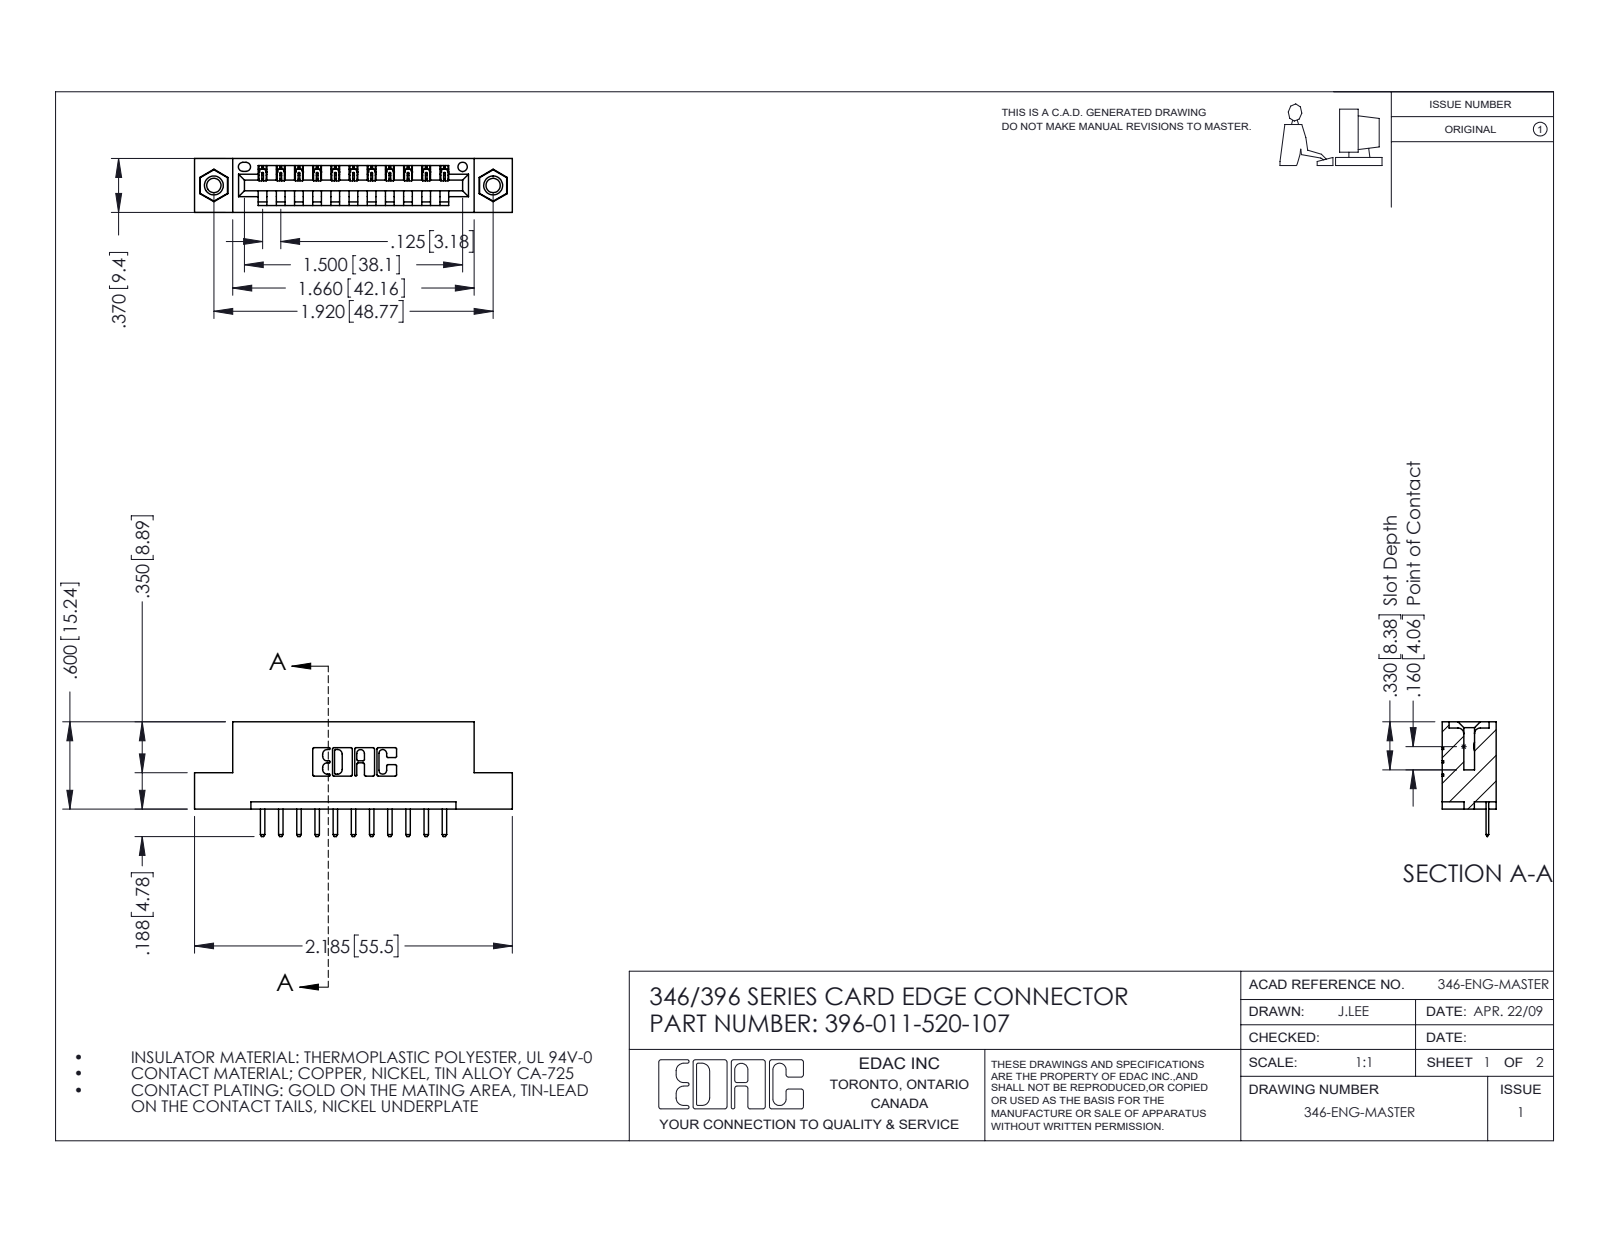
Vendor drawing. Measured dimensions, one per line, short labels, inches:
name: 396-011-520-107; 345-292-001_345-293-120; 346 Part_Flush Mounting Lugs - 0.156 Dia-TI; 345-250-001_345-250-005-103
written by: SolidWorks 2016 (CONFIG_CONTROL_DESIGN)
unit: in
bodies: 14 solids, 864 faces (570 planar, 278 cylindrical, 16 other)
size: 2.185 × 0.788 × 0.37
volume: 0.308 in³; area: 9.162 in²
holes: 2× ⌀0.098, 2× ⌀0.125, 2× ⌀0.156, 1× ⌀0.064
bosses: 2× ⌀0.155
rounds: 24× R0.01, 22× R0.006, 22× R0.01, 6× R0.007, 6× R0.031, 3× R0.026, 2× R0.031, 2× R0.04
face distances: 0.25, 0.37, 0.048, 0.322, 0.148, 0.222, 0.1, 0.174, 0.072, 0.298
hole spacings: 0.246, 1.715, 1.92
